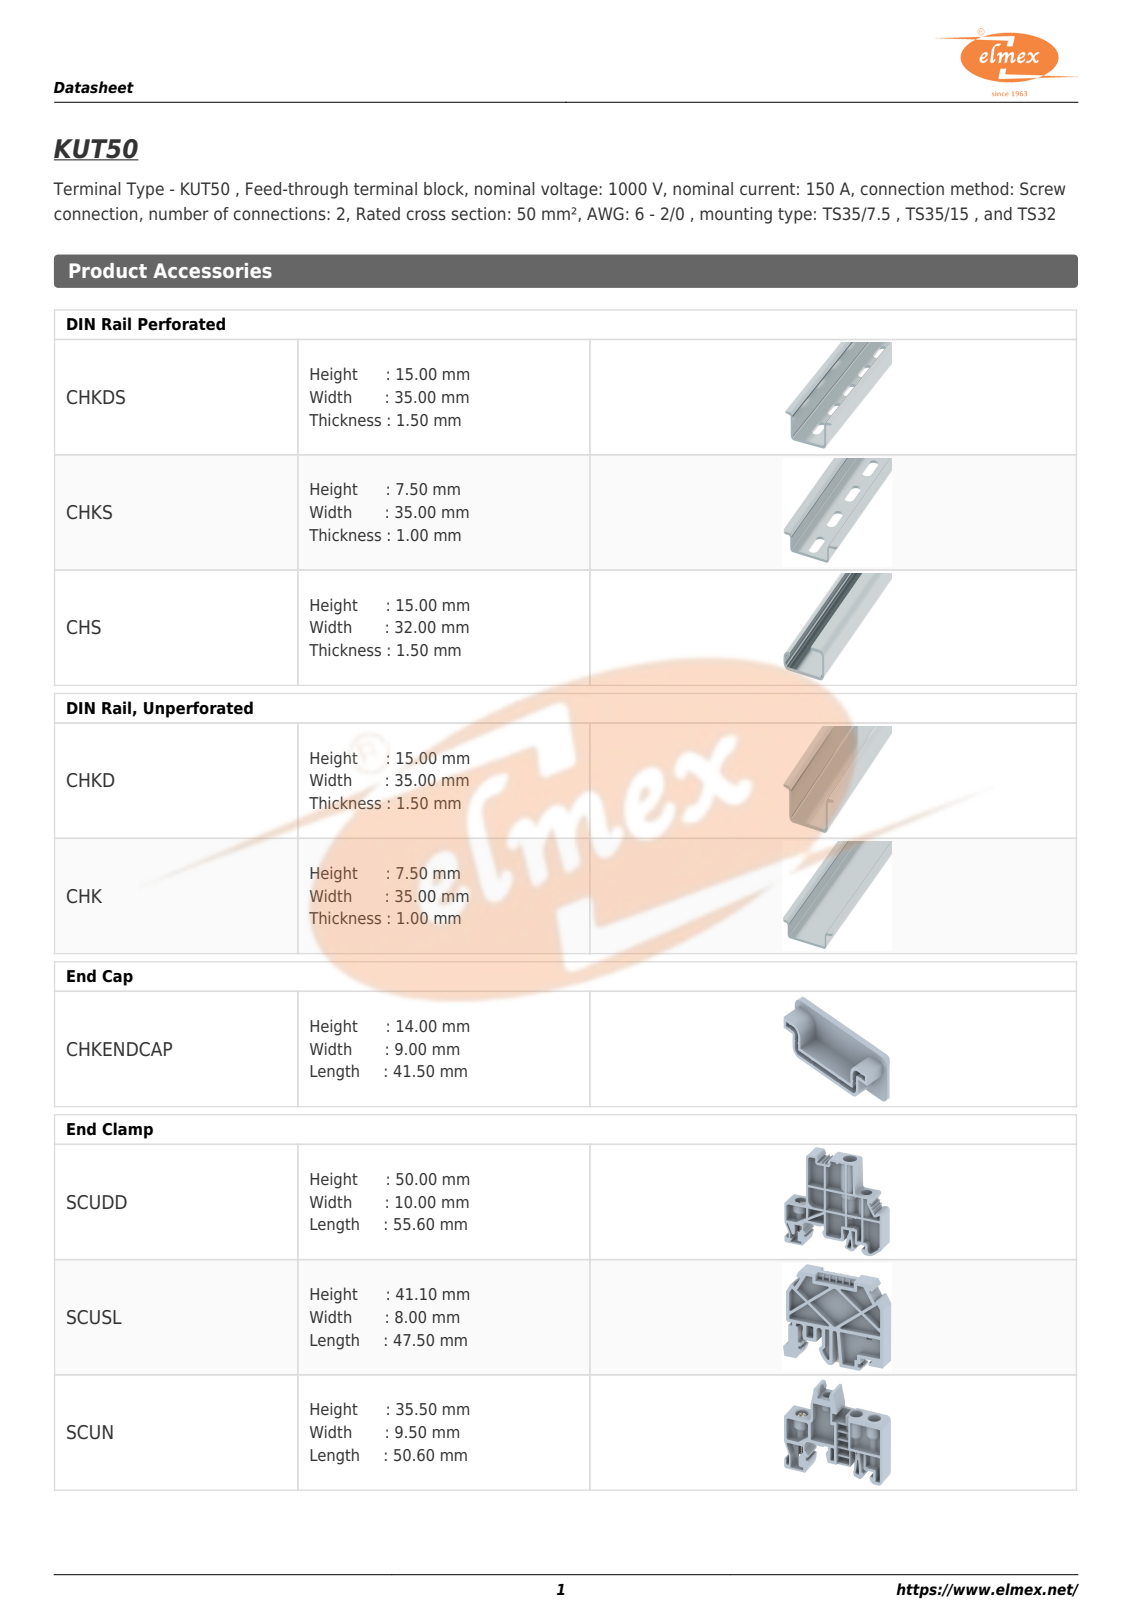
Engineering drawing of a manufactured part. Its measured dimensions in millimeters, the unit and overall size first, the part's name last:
Units: millimetres
Overall size (bounding box): 75.8 × 71 × 10.25
Partial cylindrical surfaces — rounded edges, fillets, slot ends (radius × count): R1 ×7, R0.5 ×4, R0.75 ×4, R2.5 ×1, R3 ×1, R6.82 ×1
Main face-to-face distances: 10.25, 71, 2, 68.8, 66.8, 6, 64.3, 62.3, 4.5, 28.25
Volume: 48 958 mm³ · Surface area: 12 810 mm²
Bodies: 1 solid, 65 faces (47 planar, 18 cylindrical, 0 other)
STEP written by: ST-DEVELOPER v16 (AUTOMOTIVE_DESIGN)
